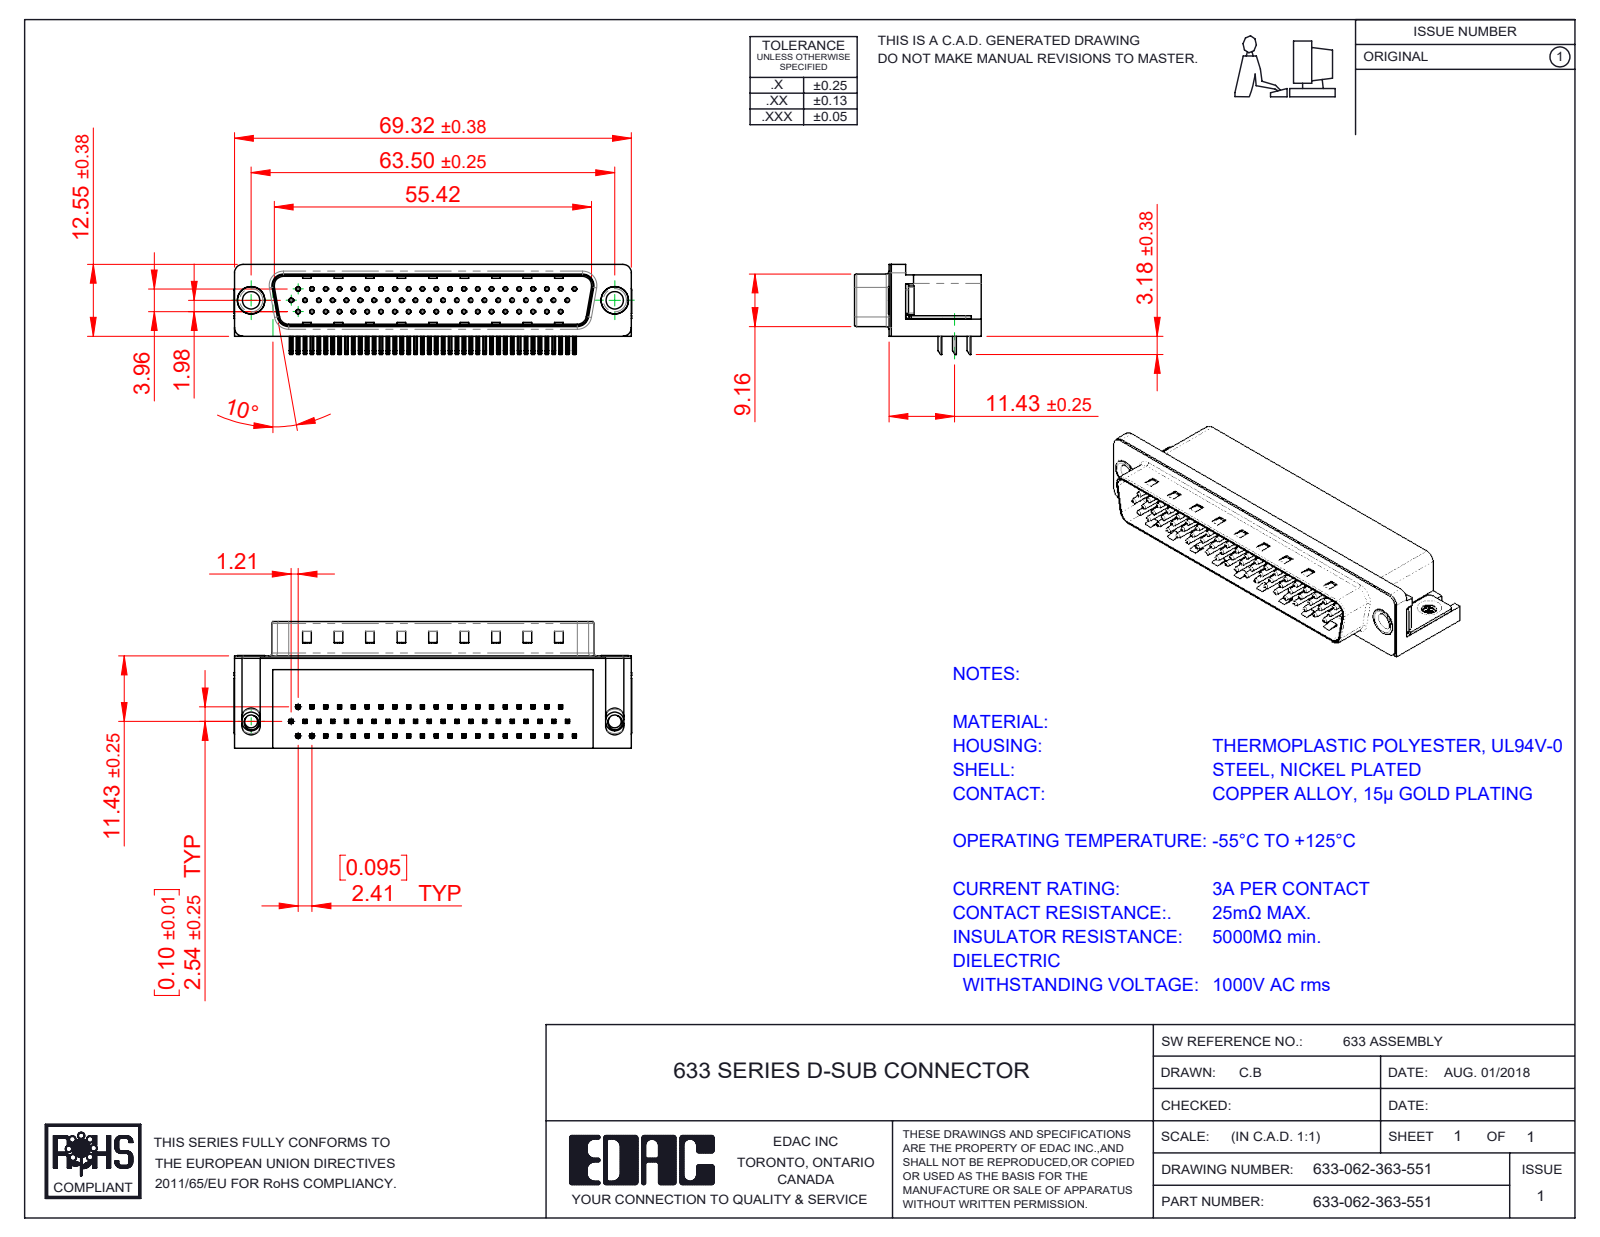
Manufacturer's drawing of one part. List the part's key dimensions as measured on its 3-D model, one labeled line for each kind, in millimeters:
Part name (STEP PRODUCT): 633 Thru Hole Rivet; 633 Contact Middle; 633 Contact Bottom; 633 Contact Top (+4 more)
STEP written by: SolidWorks 2016 (CONFIG_CONTROL_DESIGN)
Units: millimetres
Bodies: 68 solids, 5156 faces (3255 planar, 1430 cylindrical, 471 other)
Overall size (bounding box): 69.4 × 22.1 × 16.25
Volume: 11 053 mm³ · Surface area: 13 460 mm²
Round holes (diameter × count): ⌀0.35 ×62, ⌀0.8 ×62, ⌀2 ×2, ⌀3.05 ×2, ⌀4 ×2, ⌀4.8 ×2, ⌀5 ×2
Round bosses / shafts (diameter × count): ⌀0.75 ×62, ⌀4.9 ×2, ⌀4.75 ×2, ⌀3.85 ×2, ⌀3 ×2
Partial cylindrical surfaces — rounded edges, fillets, slot ends (radius × count): R0.25 ×260, R0.12 ×124, R1 ×16, R0.5 ×9, R1.6 ×8, R1.5 ×7, R0.9 ×4, R2 ×4
Main face-to-face distances: 0.4, 10.35, 15.7, 8.76, 2.9, 2.5, 2.54, 8.36, 2.1, 10.46
Hole centre spacings: 2.41, 4.82, 7.24, 9.65, 14.48, 16.89, 4.83, 7.23
